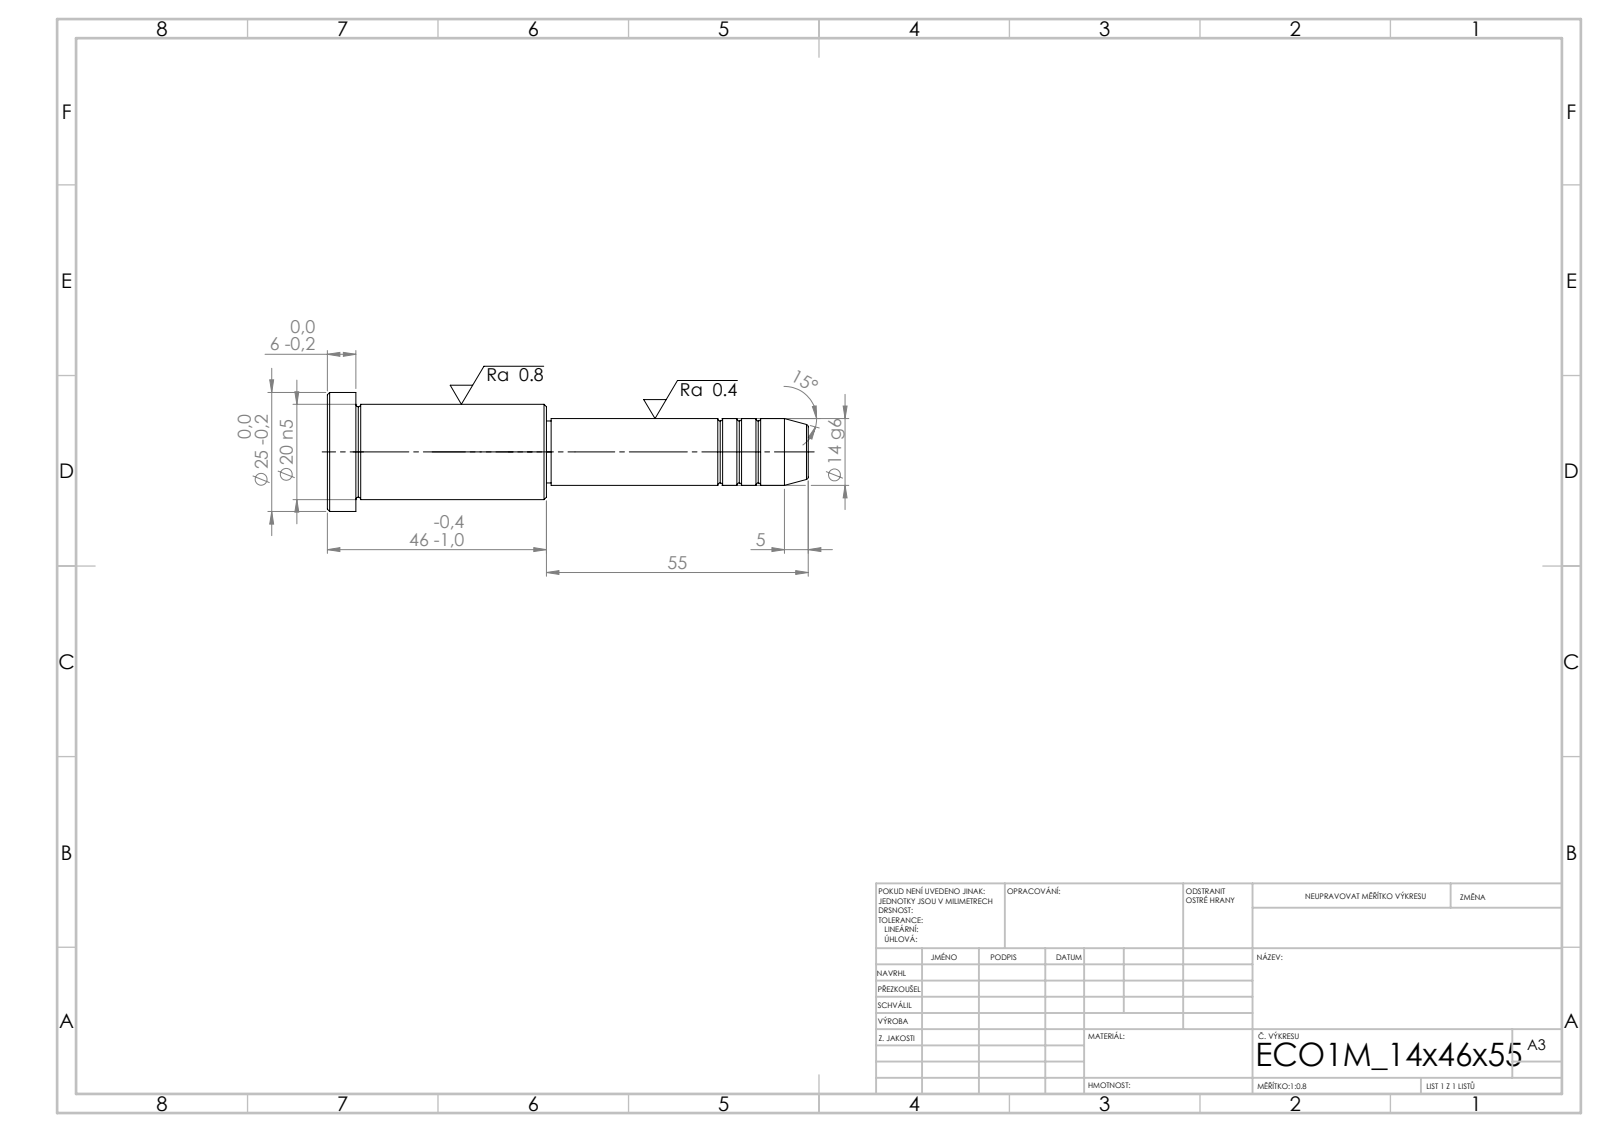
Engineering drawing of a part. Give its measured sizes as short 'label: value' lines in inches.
written by: SolidWorks 2019 (CONFIG_CONTROL_DESIGN)
unit: in
bodies: 1 solid, 43 faces (5 planar, 14 cylindrical, 24 other)
size: 3.976 × 0.984 × 0.984
volume: 1.448 in³; area: 9.936 in²
bosses: 1× ⌀0.984, 1× ⌀0.787, 1× ⌀0.551, 1× ⌀0.512
face distances: 0.236, 1.575, 1.811, 2.165, 3.74, 3.976, 2.126, 0.039, 1.614, 1.85
